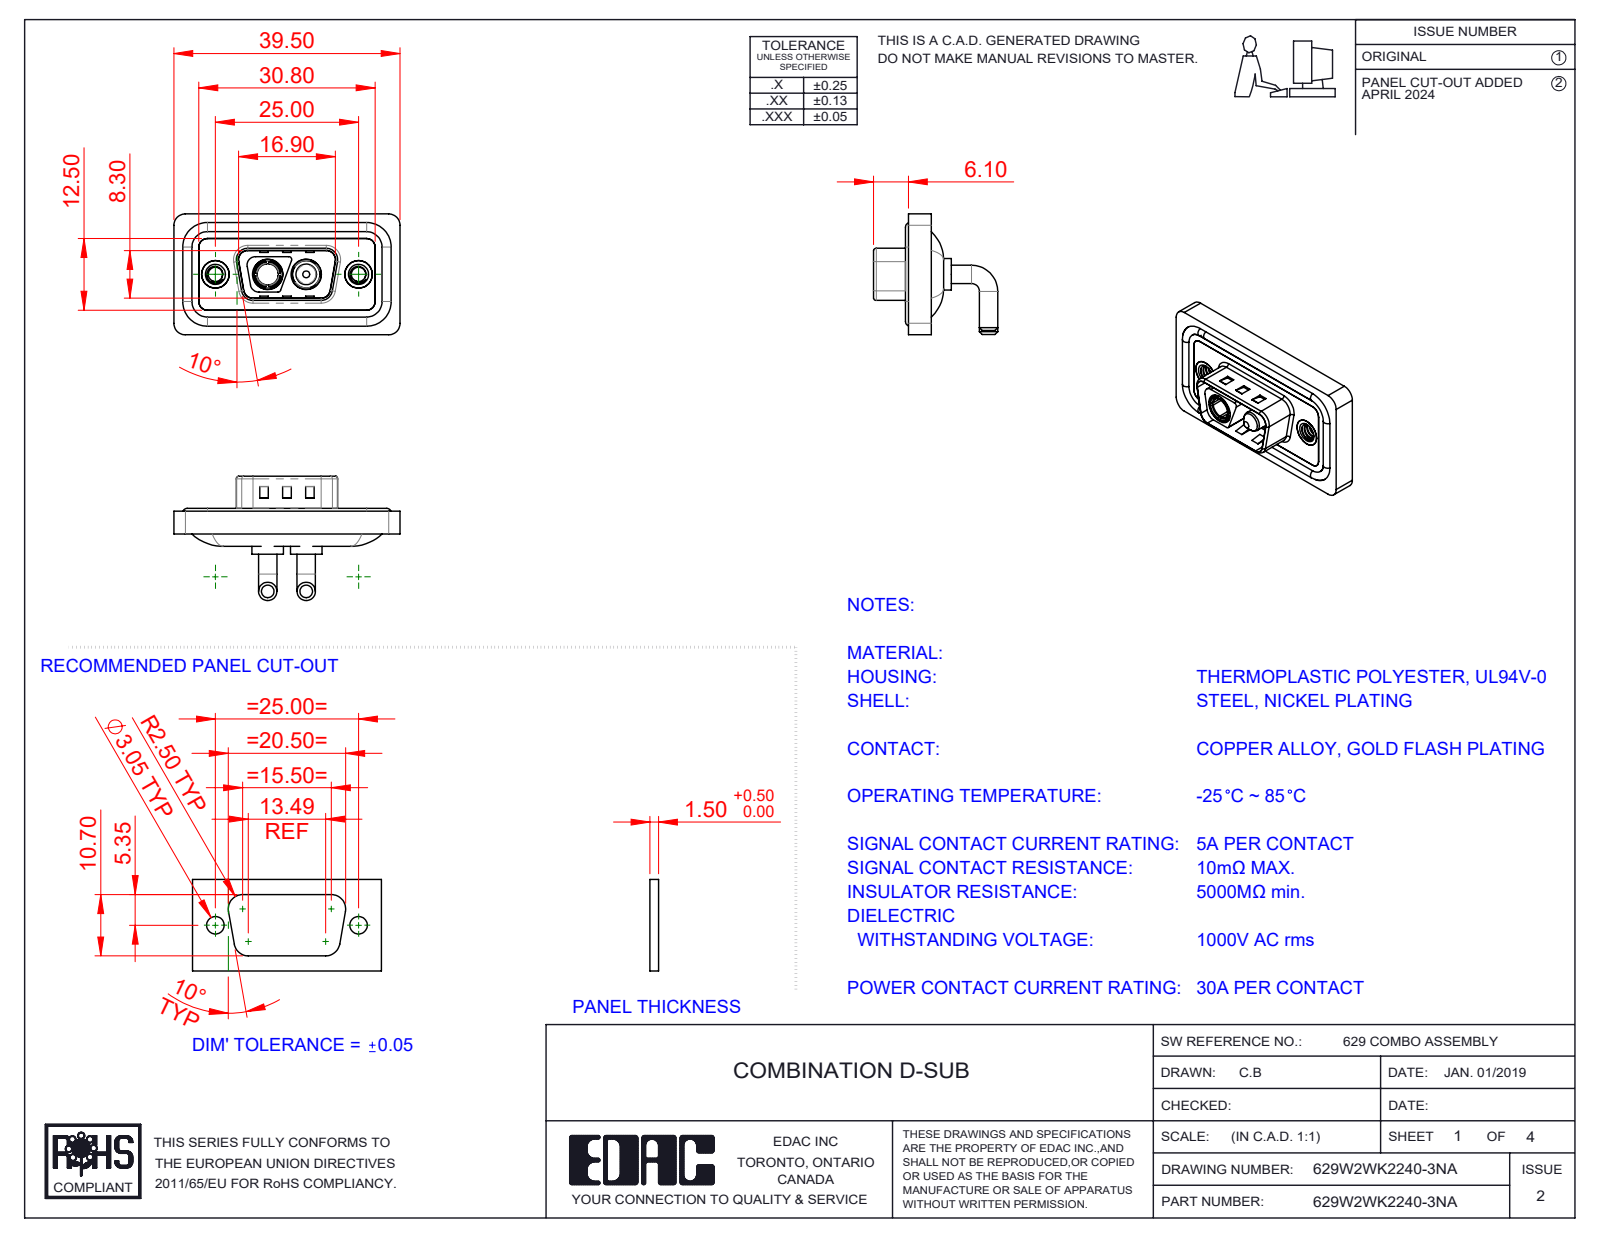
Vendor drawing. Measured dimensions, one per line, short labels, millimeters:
name: Power Socket_30A RA; 629Combo Shell Front_09 Contacts; 629Combo Shell Rear_09 Contacts; 629Combo Waterproof Housing_09 Contacts (+4 more)
written by: SolidWorks 2023 (CONFIG_CONTROL_DESIGN)
unit: mm
bodies: 11 solids, 536 faces (189 planar, 229 cylindrical, 118 other)
size: 39.5 × 21.7 × 21.1
volume: 4 743 mm³; area: 7 573 mm²
holes: 2× ⌀2.5, 2× ⌀4, 2× ⌀4.8, 2× ⌀4.85, 2× ⌀5, 2× ⌀5.3, 1× ⌀3.7
bosses: 4× ⌀3.2, 4× ⌀1.6, 2× ⌀5.5, 2× ⌀5.2, 2× ⌀4.9, 2× ⌀4.75, 2× ⌀3.75, 1× ⌀4.96
rounds: 20× R1.5, 18× R2, 10× R0.5, 8× R1.6, 4× R0.25, 4× R0.6, 4× R0.65, 4× R0.9
face distances: 0.4, 2.9, 1.1, 0.8, 2.1, 2.5, 3.1, 1.6, 4.5, 1.5
hole spacings: 9.14, 15.86, 6.72, 25
